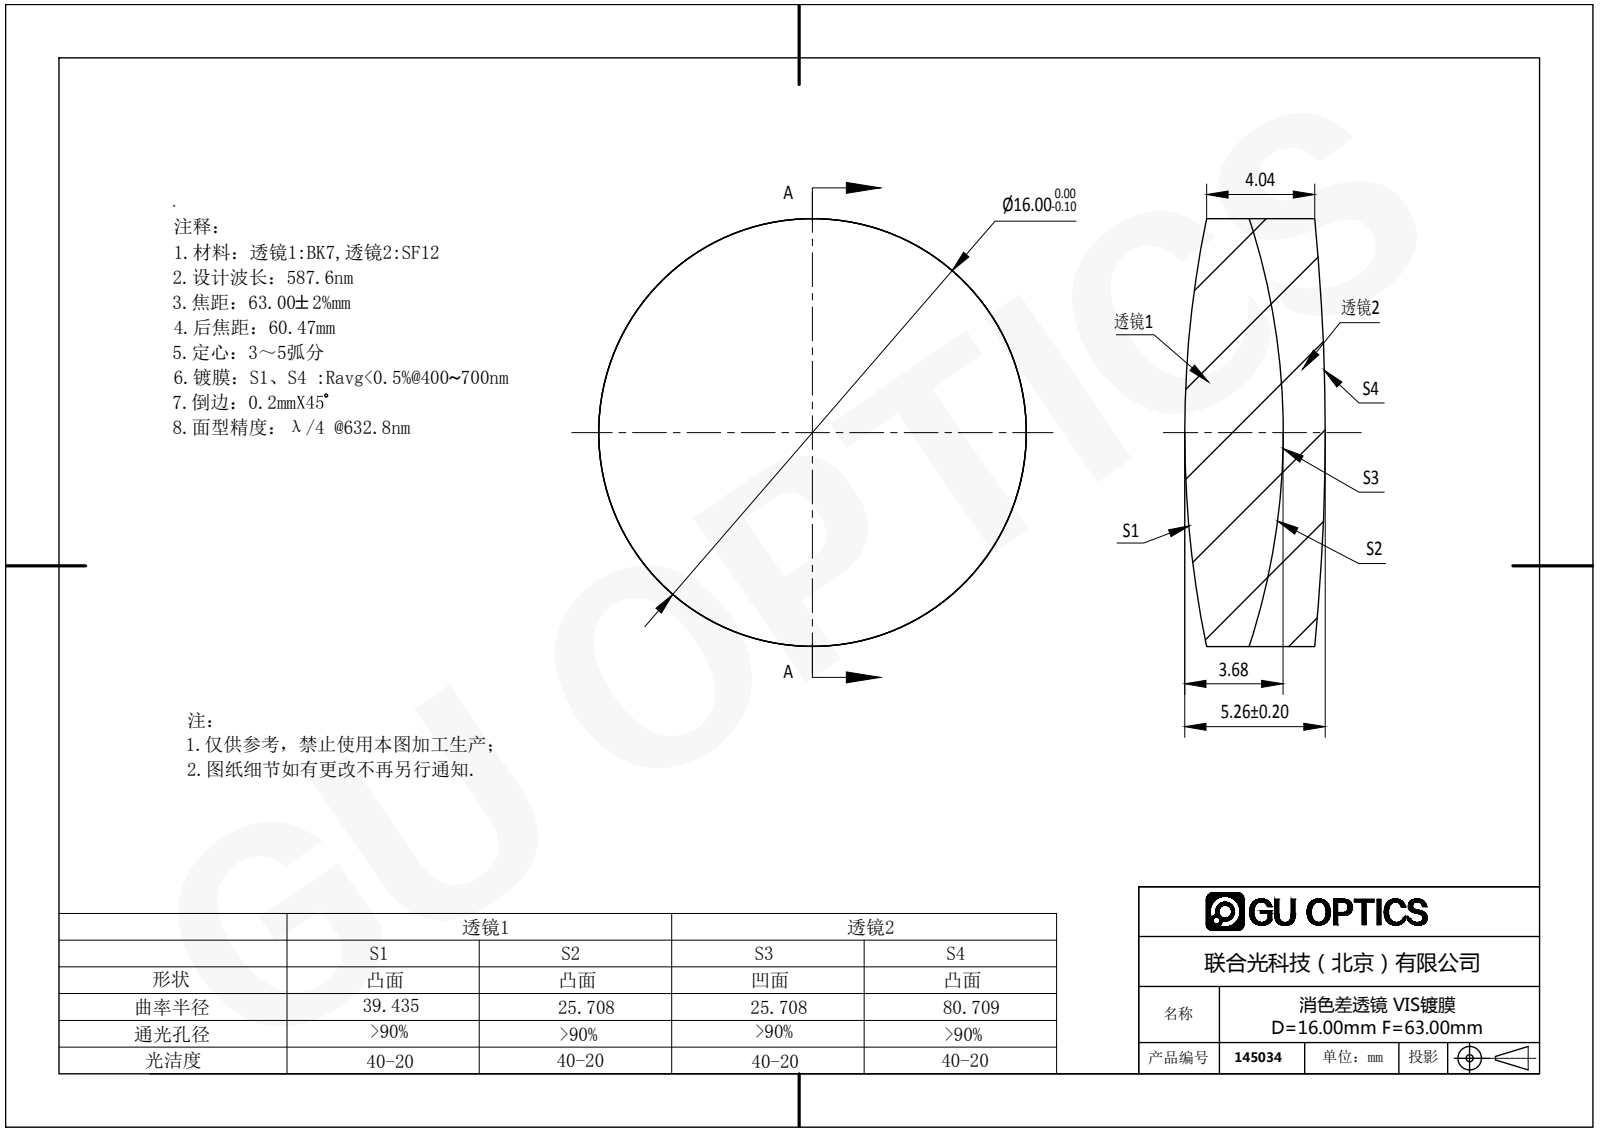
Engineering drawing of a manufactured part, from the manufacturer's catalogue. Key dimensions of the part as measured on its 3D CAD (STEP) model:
Part name (STEP PRODUCT): 145034
STEP written by: SolidWorks 2016 (AUTOMOTIVE_DESIGN)
Units: millimetres
Bodies: 2 solids, 12 faces (0 planar, 4 cylindrical, 8 other)
Overall size (bounding box): 16 × 16 × 5.26
Volume: 936 mm³ · Surface area: 1 020 mm²
Round bosses / shafts (diameter × count): ⌀16 ×1
